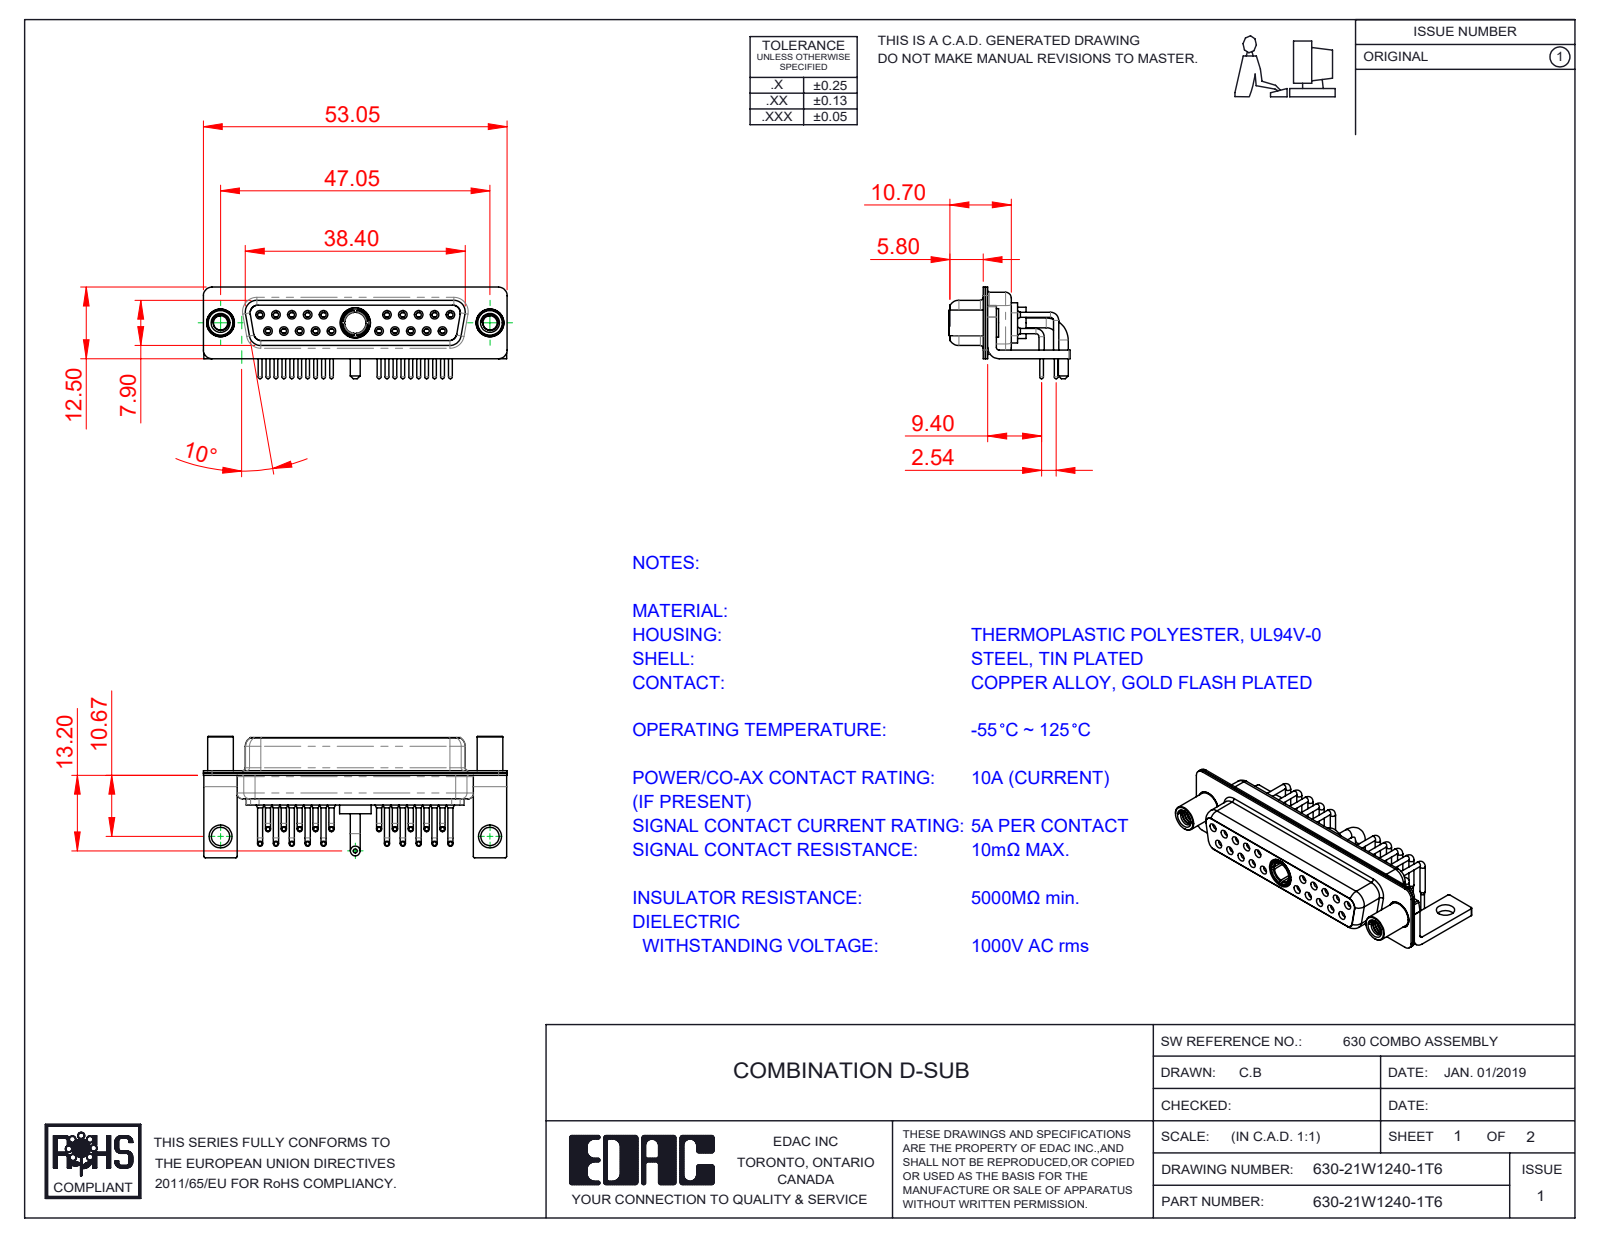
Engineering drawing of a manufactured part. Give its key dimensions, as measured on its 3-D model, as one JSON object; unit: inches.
{"part_name": "630Combo Shell Front_25 Contacts; 630Combo Housing_21W1; 630Combo Threaded Standoff_D; 630Combo Contact Row 2 (+5 more)", "step_written_by": "SolidWorks 2020 (CONFIG_CONTROL_DESIGN)", "units": "inches", "bodies": {"solids": 29, "faces": 1515, "planar": 418, "cylindrical": 694, "other": 403}, "overall_size": [2.089, 0.835, 0.63], "volume_in3": 0.266, "surface_area_in2": 15.85, "round_holes": [[0.035, 20], [0.043, 20], [0.059, 20], [0.079, 20], [0.063, 10], [0.067, 10], [0.191, 3], [0.098, 2], [0.126, 2], [0.157, 2], [0.159, 2], [0.146, 1]], "round_bosses_or_shafts": [[0.035, 20], [0.026, 20], [0.063, 10], [0.197, 2], [0.195, 2], [0.189, 2], [0.177, 2], [0.067, 2]], "partial_cylinders_radius": [[0.01, 16], [0.059, 16], [0.079, 13], [0.053, 8], [0.063, 8], [0.02, 5], [0.024, 4], [0.026, 4]], "face_to_face_distances": [0.016, 0.018, 0.055, 0.333, 0.031, 0.071, 0.35, 0.244, 0.278, 0.059], "hole_center_spacings": [0.124, 0.109, 0.218, 0.327, 0.198, 0.763, 0.826, 0.872]}
